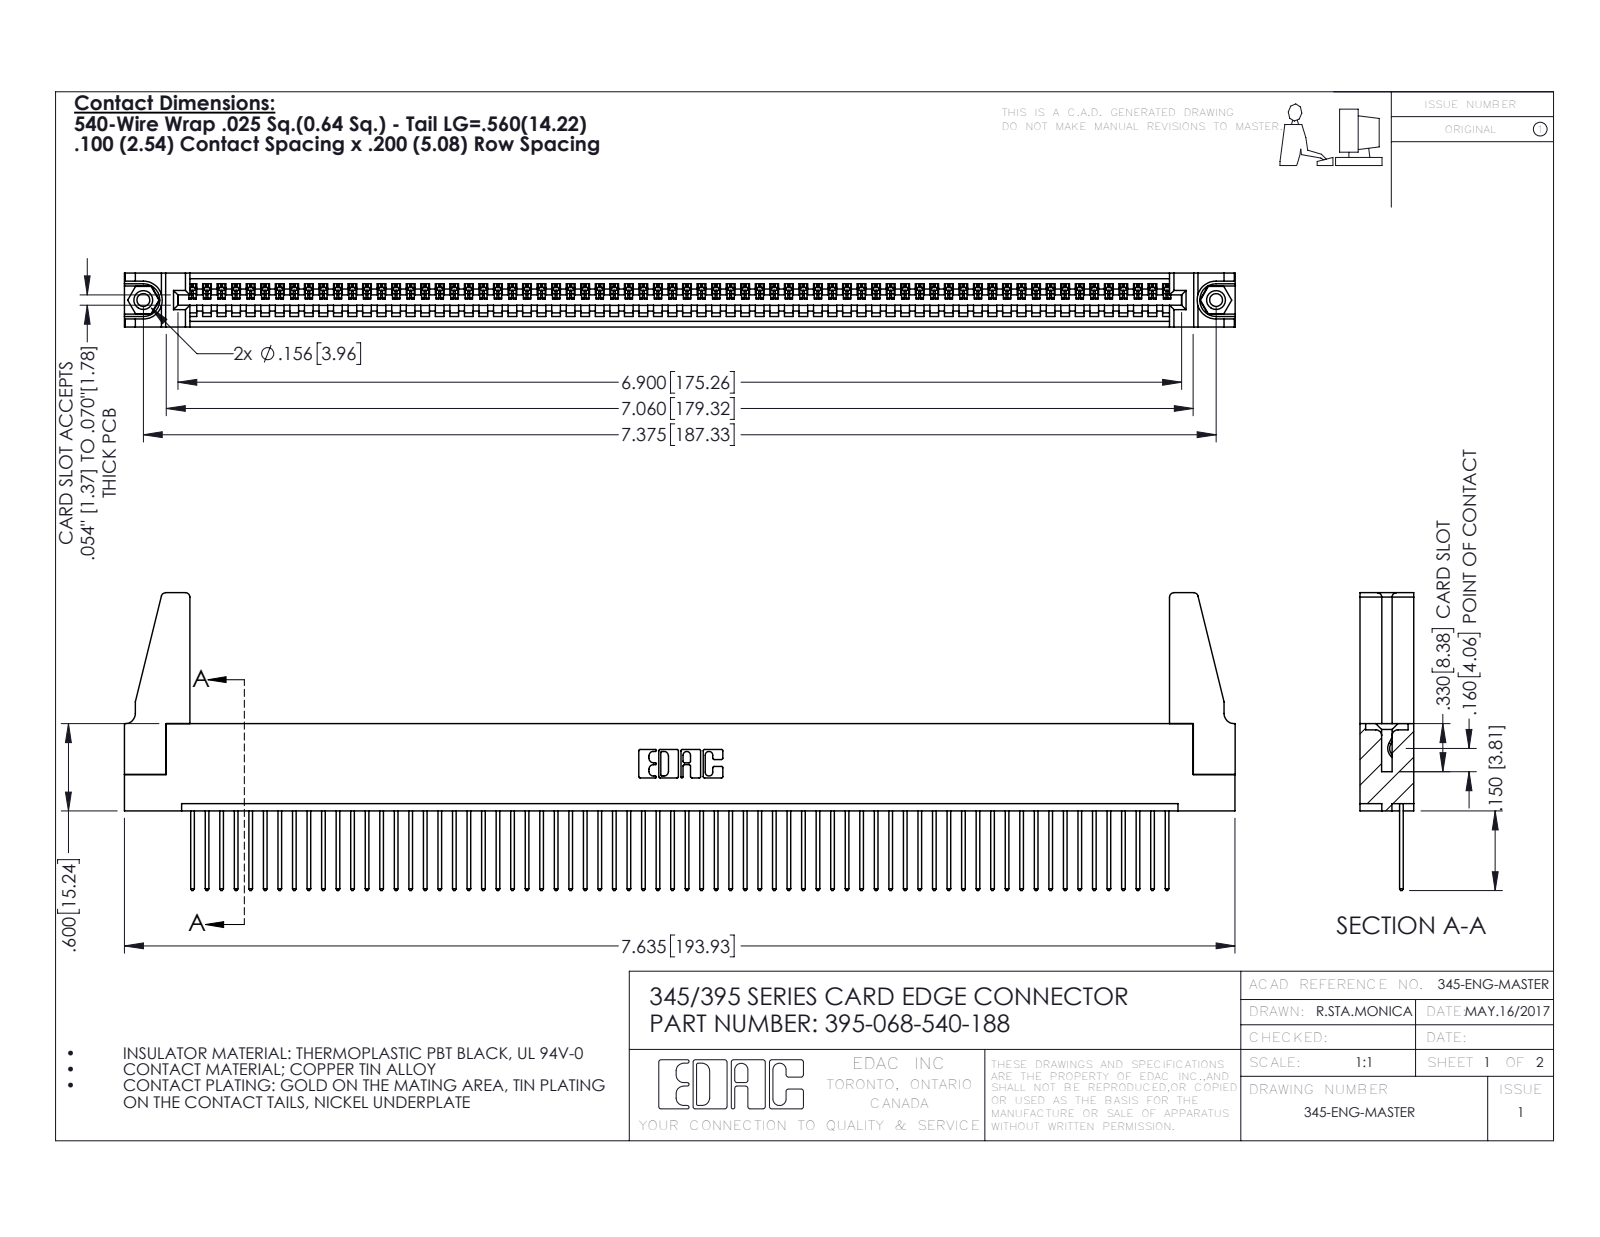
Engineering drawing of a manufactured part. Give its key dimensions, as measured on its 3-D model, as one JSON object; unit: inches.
{"part_name": "345 Part_Flush Mounting Lugs - 0.156 Dia-TH; 395-068-540-188; 345-220-078_345-220-088; 345-292-001_345-293-140 (+1 more)", "step_written_by": "SolidWorks 2016 (CONFIG_CONTROL_DESIGN)", "units": "inches", "bodies": {"solids": 73, "faces": 4194, "planar": 2872, "cylindrical": 1306, "other": 16}, "overall_size": [7.636, 2.047, 0.37], "volume_in3": 1.341, "surface_area_in2": 45, "round_holes": [[0.089, 2], [0.125, 2], [0.156, 2], [0.064, 1]], "round_bosses_or_shafts": [[0.155, 2]], "partial_cylinders_radius": [[0.006, 136], [0.01, 136], [0.01, 22], [0.03, 8], [0.007, 6], [0.031, 6], [0.026, 3], [0.031, 2]], "face_to_face_distances": [0.072, 0.298, 0.37, 0.098, 0.272, 0.025, 0.2, 0.225, 0.149, 0.072], "hole_center_spacings": [0.27, 7.139, 7.375]}
